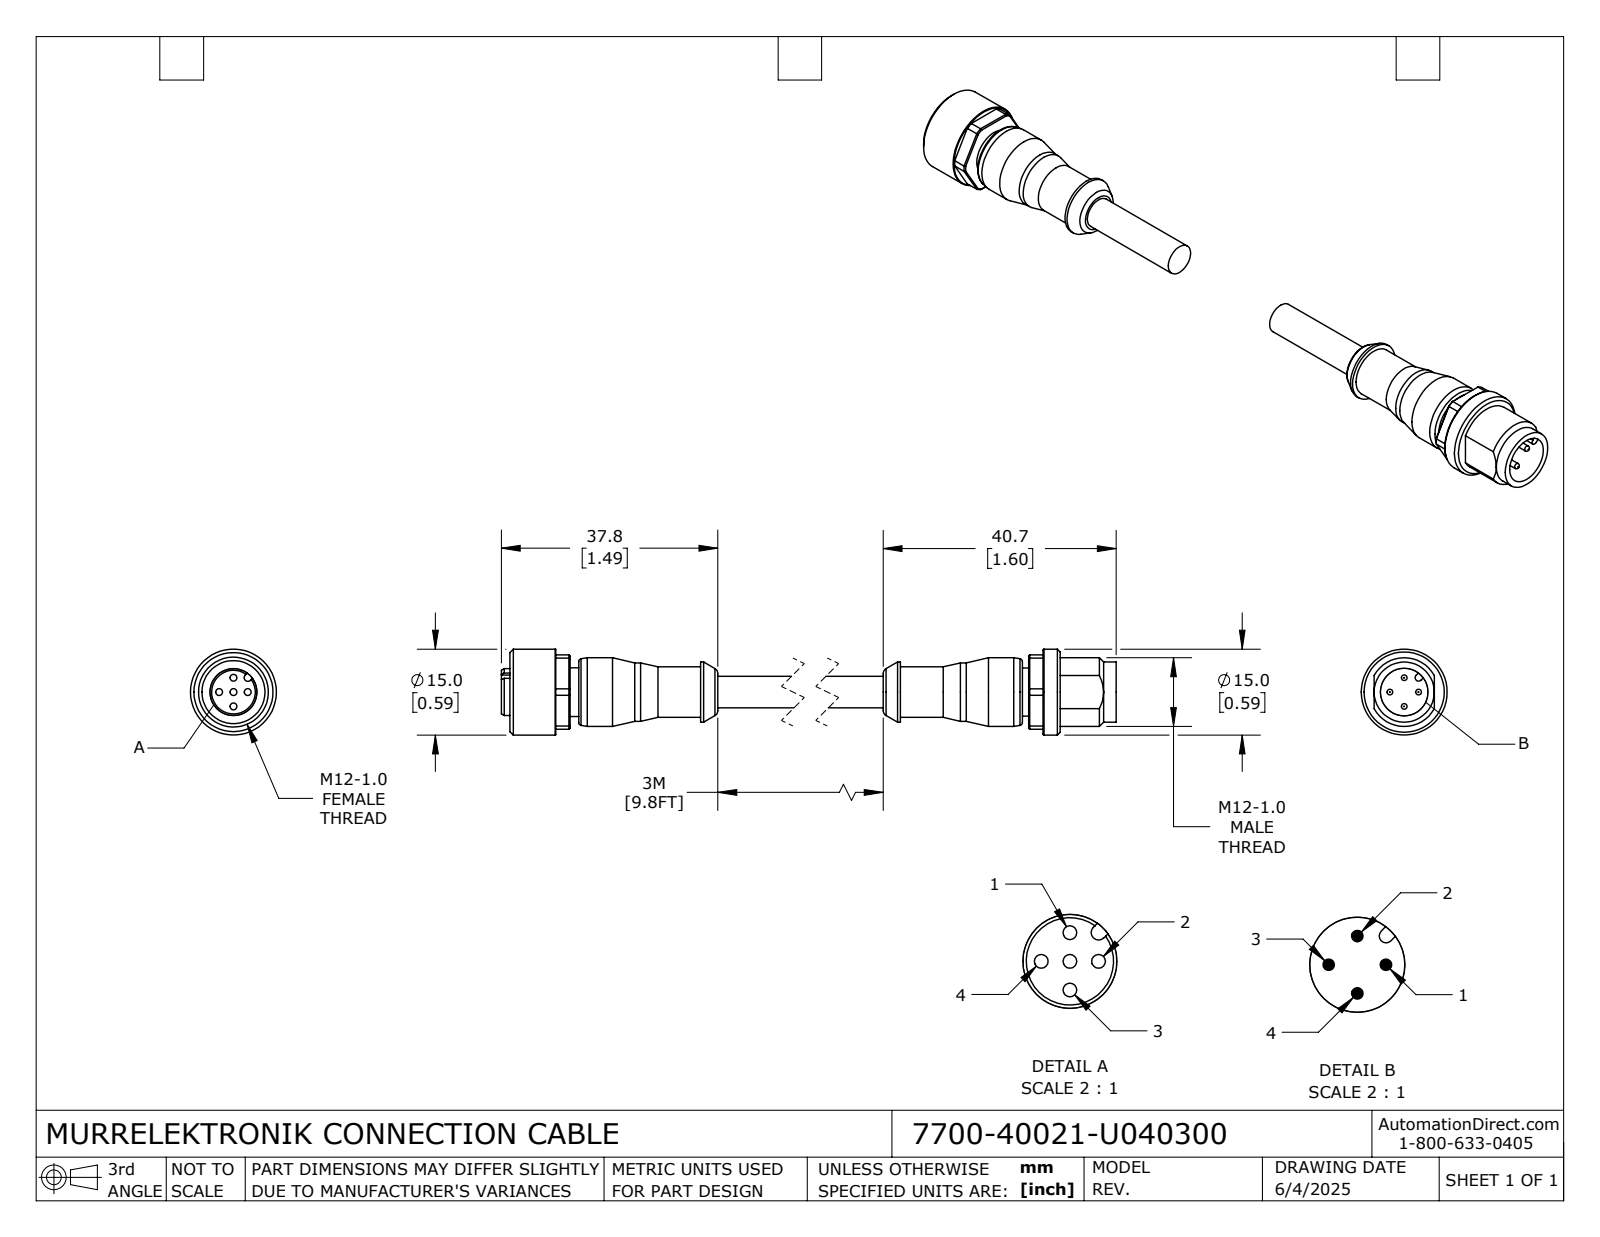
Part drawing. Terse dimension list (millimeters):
name: 7700-40021-U040300_MALE; 7700-40021-U040300_FEMALE; 7700-40021-U040300
written by: SolidWorks 2024 (CONFIG_CONTROL_DESIGN)
unit: mm
bodies: 2 solids, 191 faces (59 planar, 71 cylindrical, 61 other)
size: 143.5 × 15 × 15
volume: 7 988 mm³; area: 5 143 mm²
holes: 5× ⌀1.2, 1× ⌀8.3, 1× ⌀11
bosses: 4× ⌀1, 1× ⌀15, 1× ⌀12, 1× ⌀10.5, 1× ⌀10.2, 1× ⌀8.8, 1× ⌀8.5, 1× ⌀8.4
rounds: 1× R0.6, 1× R0.65, 1× R7.2
face distances: 13, 3, 116.2, 10.5, 125.6, 12, 121.7, 7.5, 1.5, 2.5
hole spacings: 2.5, 3.54, 5
